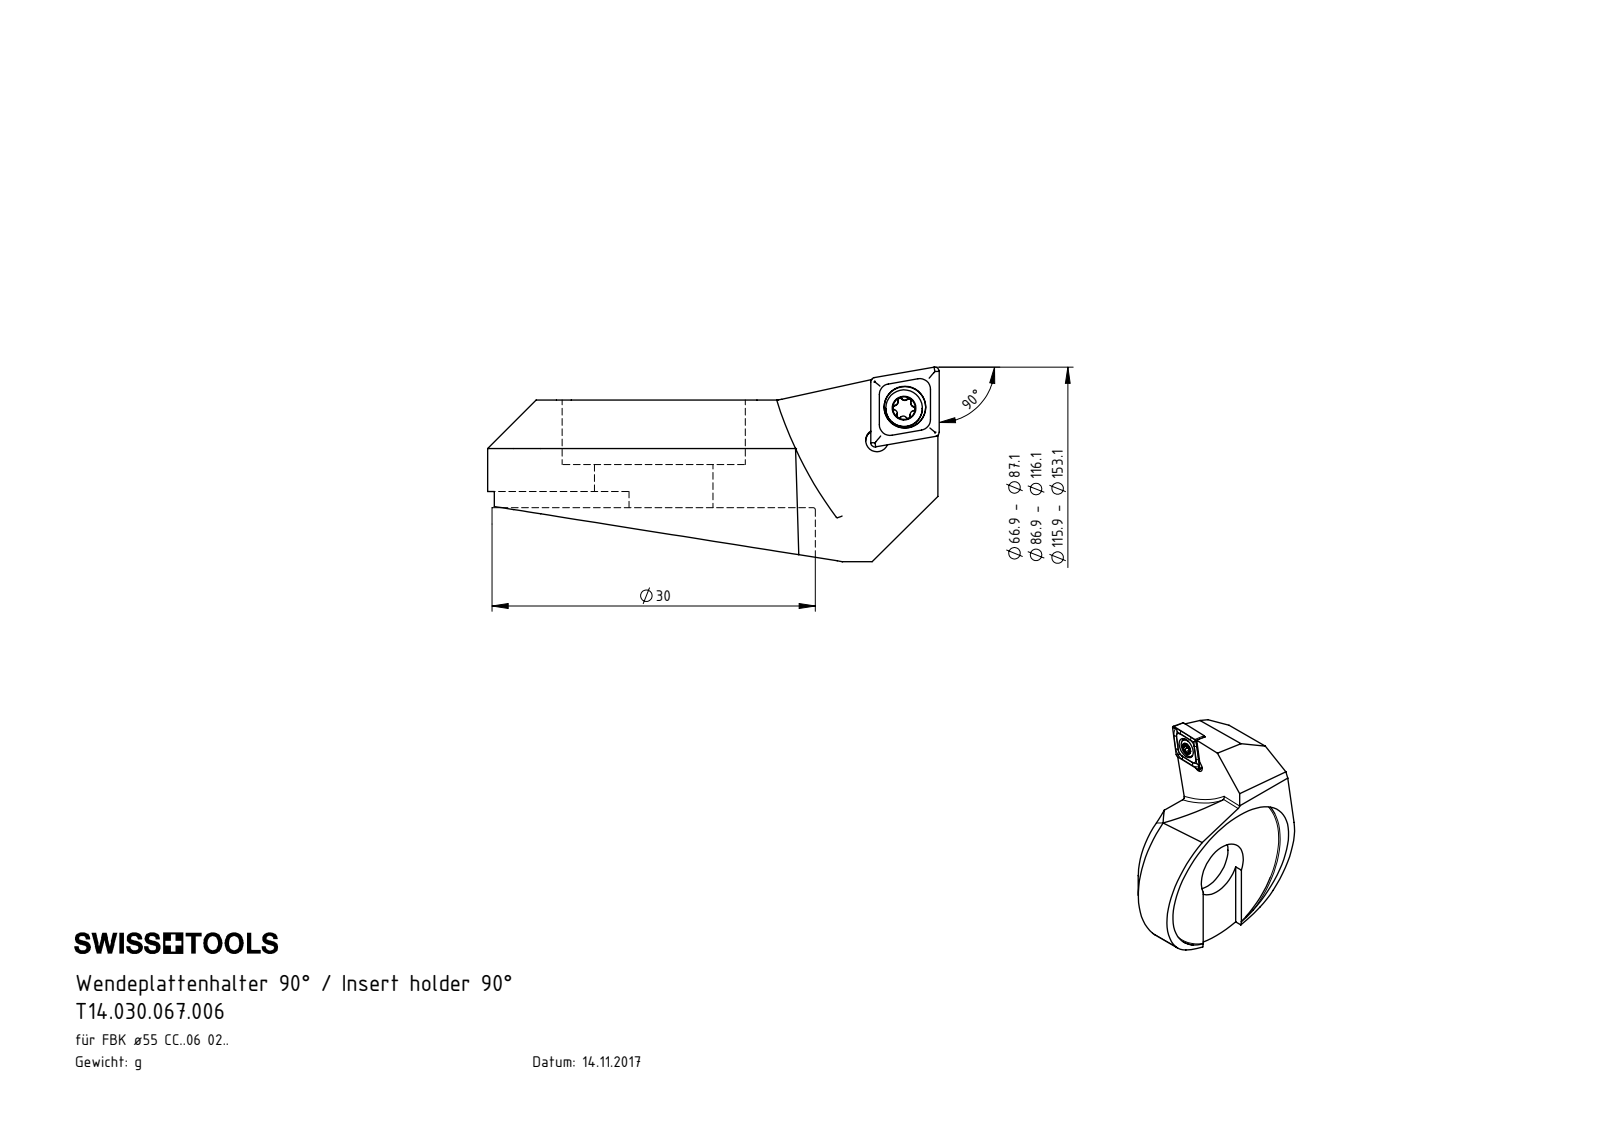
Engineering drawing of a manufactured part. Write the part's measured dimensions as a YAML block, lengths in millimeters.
part_name: "CCMT060204; F55.WCA.001.013; F55-WCA.001.013_D_fertigbearbeitet; WCA-ER2.001.005_A"
step_written_by: "SolidWorks 2017 (AUTOMOTIVE_DESIGN)"
units: millimeters
bodies: {solids: 3, faces: 112, planar: 39, cylindrical: 30, other: 43}
overall_size: [41.9, 33.1, 18.05]
volume: 7725
surface_area: 3934
round_holes:
  - {diameter: 2.05, count: 1}
  - {diameter: 2.1, count: 1}
  - {diameter: 2.8, count: 1}
  - {diameter: 3.85, count: 1}
  - {diameter: 11, count: 1}
  - {diameter: 17, count: 1}
  - {diameter: 30, count: 1}
round_bosses_or_shafts:
  - {diameter: 3.4, count: 1}
  - {diameter: 2.5, count: 1}
partial_cylinders:
  - {radius: 0.21, count: 6}
  - {radius: 0.36, count: 5}
  - {radius: 0.5, count: 2}
  - {radius: 10, count: 2}
  - {radius: 0.36, count: 1}
  - {radius: 5, count: 1}
  - {radius: 16.55, count: 1}
  - {radius: 20.9, count: 1}
face_to_face_distances: [10, 6, 4, 8.5, 2.5, 1.5, 2.18, 5, 15, 9]
hole_center_spacings: [3.91, 4.04]
